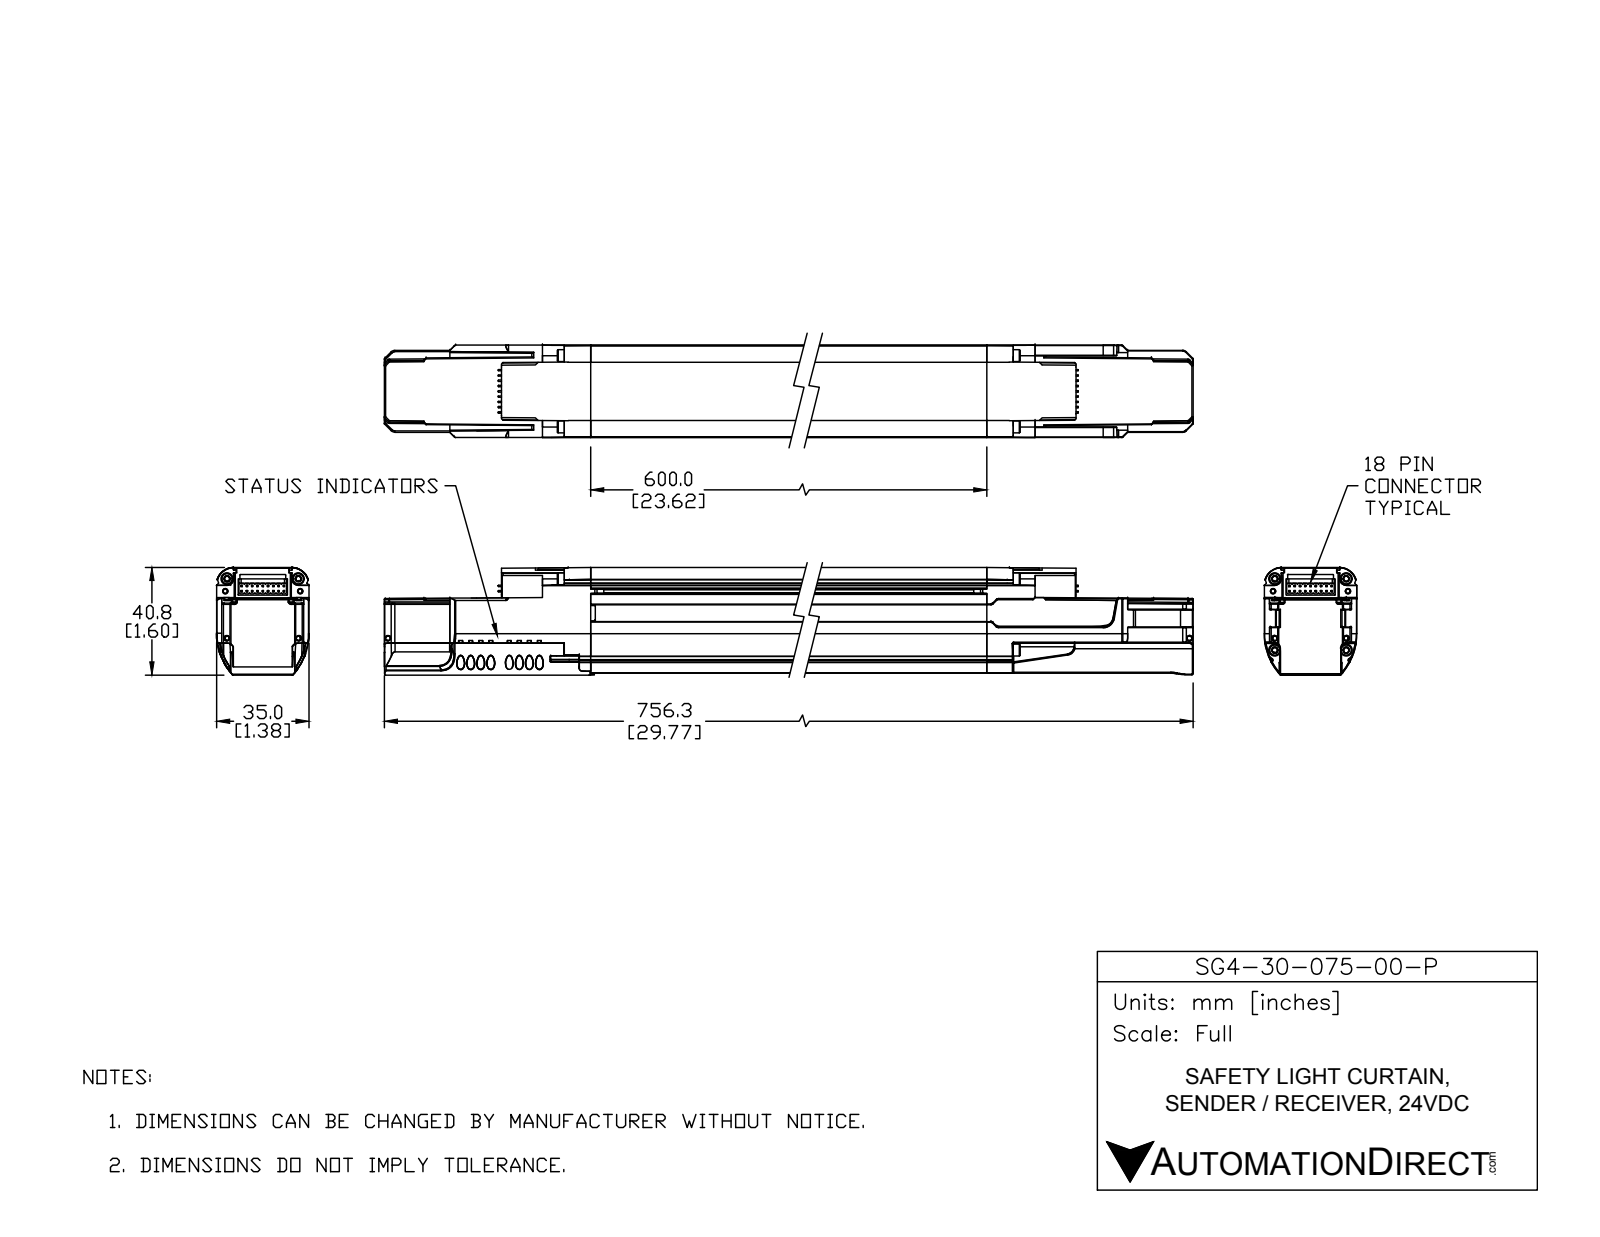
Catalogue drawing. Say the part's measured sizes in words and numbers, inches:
The part is named "SG4-30-075-OO-P". Its 3-D file was written by "SolidWorks 2017 (AUTOMOTIVE_DESIGN)". It is 16 solids with 534 faces: 362 planar, 110 cylindrical and 62 other. Overall it measures 29.763 by 2.58 by 2.023 inches. Its volume is 55.9 cubic inches and its surface area 320.5 square inches. Round holes: 6 of diameter 0.07, 4 of diameter 0.1, 4 of diameter 0.165, 4 of diameter 0.209, 4 of diameter 0.26, 1 of diameter 0.065, 1 of diameter 0.065. Round bosses or shafts: 4 of diameter 0.394, 4 of diameter 0.197. Partial cylindrical surfaces (rounded edges, fillets, slot ends): 16 of radius 0.106, 8 of radius 0.118, 4 of radius 0.1, 4 of radius 0.11, 2 of radius 0.08, 2 of radius 0.12, 2 of radius 0.123, 2 of radius 0.125. The main face-to-face distances are 0.06, 0.084, 0.024, 1.49, 1.466, 1.55, 1.057, 0.481, 0.985, 1.009. The hole center spacings are 0.569, 22.035, 0.02, 0.204, 0.207, 0.207, 0.227, 0.71.
